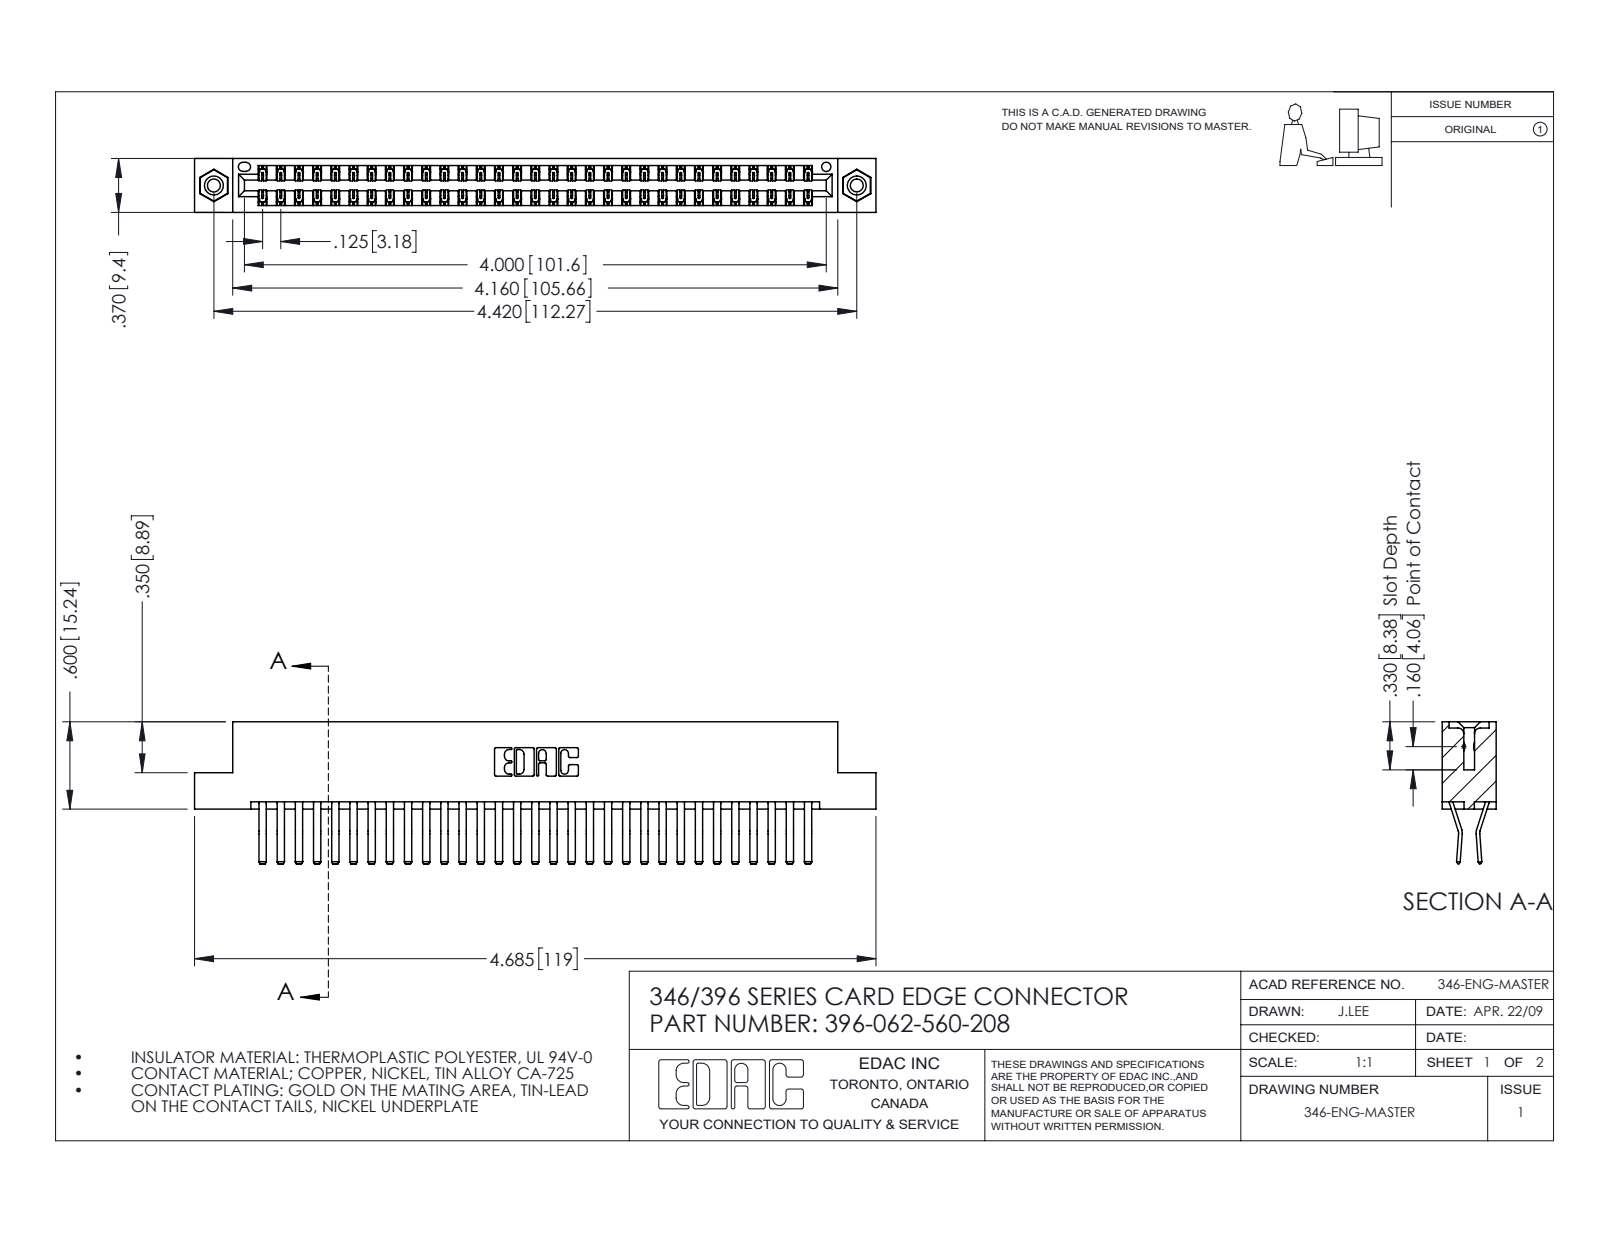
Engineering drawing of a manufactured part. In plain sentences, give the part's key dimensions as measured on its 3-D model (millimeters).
The part is named "396-062-560-208; 346 Part_Flush Mounting Lugs - 0.156 Dia-TI; 345-250-001_345-250-003-102; 345-292-001_560 Tail". Its 3-D file was written by "SolidWorks 2016 (CONFIG_CONTROL_DESIGN)". It is 65 solids with 3530 faces: 2278 planar, 1236 cylindrical and 16 other. Overall it measures 119 by 24.8 by 9.4 millimeters. Its volume is 11 900 cubic millimeters and its surface area 17 320 square millimeters. Round holes: 2 of diameter 2.3, 2 of diameter 3.2, 2 of diameter 4, 1 of diameter 1.6. Round bosses or shafts: 2 of diameter 3.9. Partial cylindrical surfaces (rounded edges, fillets, slot ends): 93 of radius 0.2, 22 of radius 0.3, 6 of radius 0.2, 6 of radius 0.8, 3 of radius 0.7, 2 of radius 0.3, 2 of radius 0.4, 2 of radius 0.6. The main face-to-face distances are 1.2, 8.2, 9.4, 6.4, 0.6, 1.8, 7.6, 7, 3.8, 5.6. The hole center spacings are 6.2, 107, 112.3.
